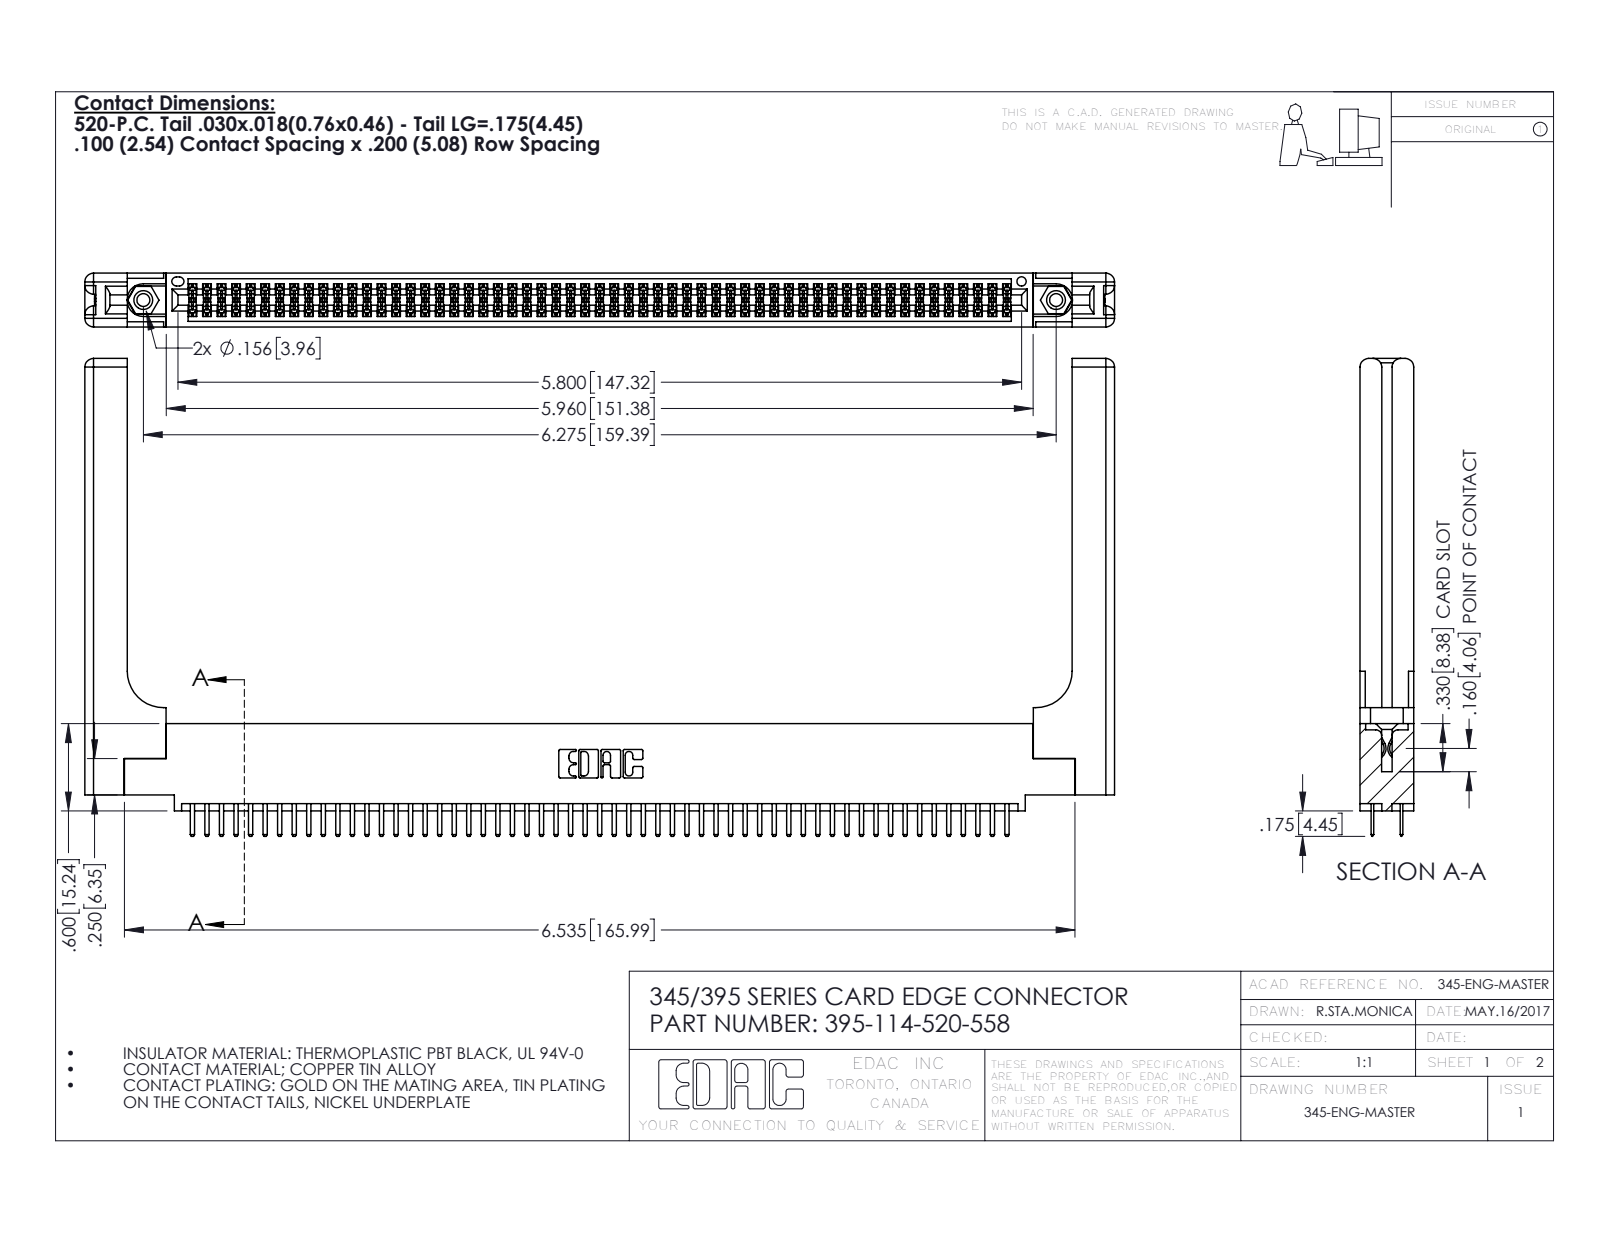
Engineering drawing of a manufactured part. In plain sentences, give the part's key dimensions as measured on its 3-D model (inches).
The part is named "345 Part_0.110 Offset - 0.156 Dia-TH; 345-250-001_345-250-001-102; 395-114-520-558; 345-292-001_345-293-120 (+1 more)". Its 3-D file was written by "SolidWorks 2016 (CONFIG_CONTROL_DESIGN)". It is 119 solids with 6542 faces: 4222 planar, 2260 cylindrical and 60 other. Overall it measures 7.079 by 3.285 by 0.37 inches. Its volume is 1.584 cubic inches and its surface area 48.33 square inches. Round holes: 2 of diameter 0.089, 2 of diameter 0.125, 2 of diameter 0.156, 1 of diameter 0.064. Round bosses or shafts: 2 of diameter 0.155. Partial cylindrical surfaces (rounded edges, fillets, slot ends): 171 of radius 0.006, 118 of radius 0.01, 22 of radius 0.01, 16 of radius 0.06, 6 of radius 0.007, 6 of radius 0.031, 3 of radius 0.026, 2 of radius 0.014. The main face-to-face distances are 0.072, 0.298, 0.37, 0.2, 0.098, 0.272, 0.025, 0.225, 0.022, 0.072. The hole center spacings are 0.27, 6.039, 6.275.
